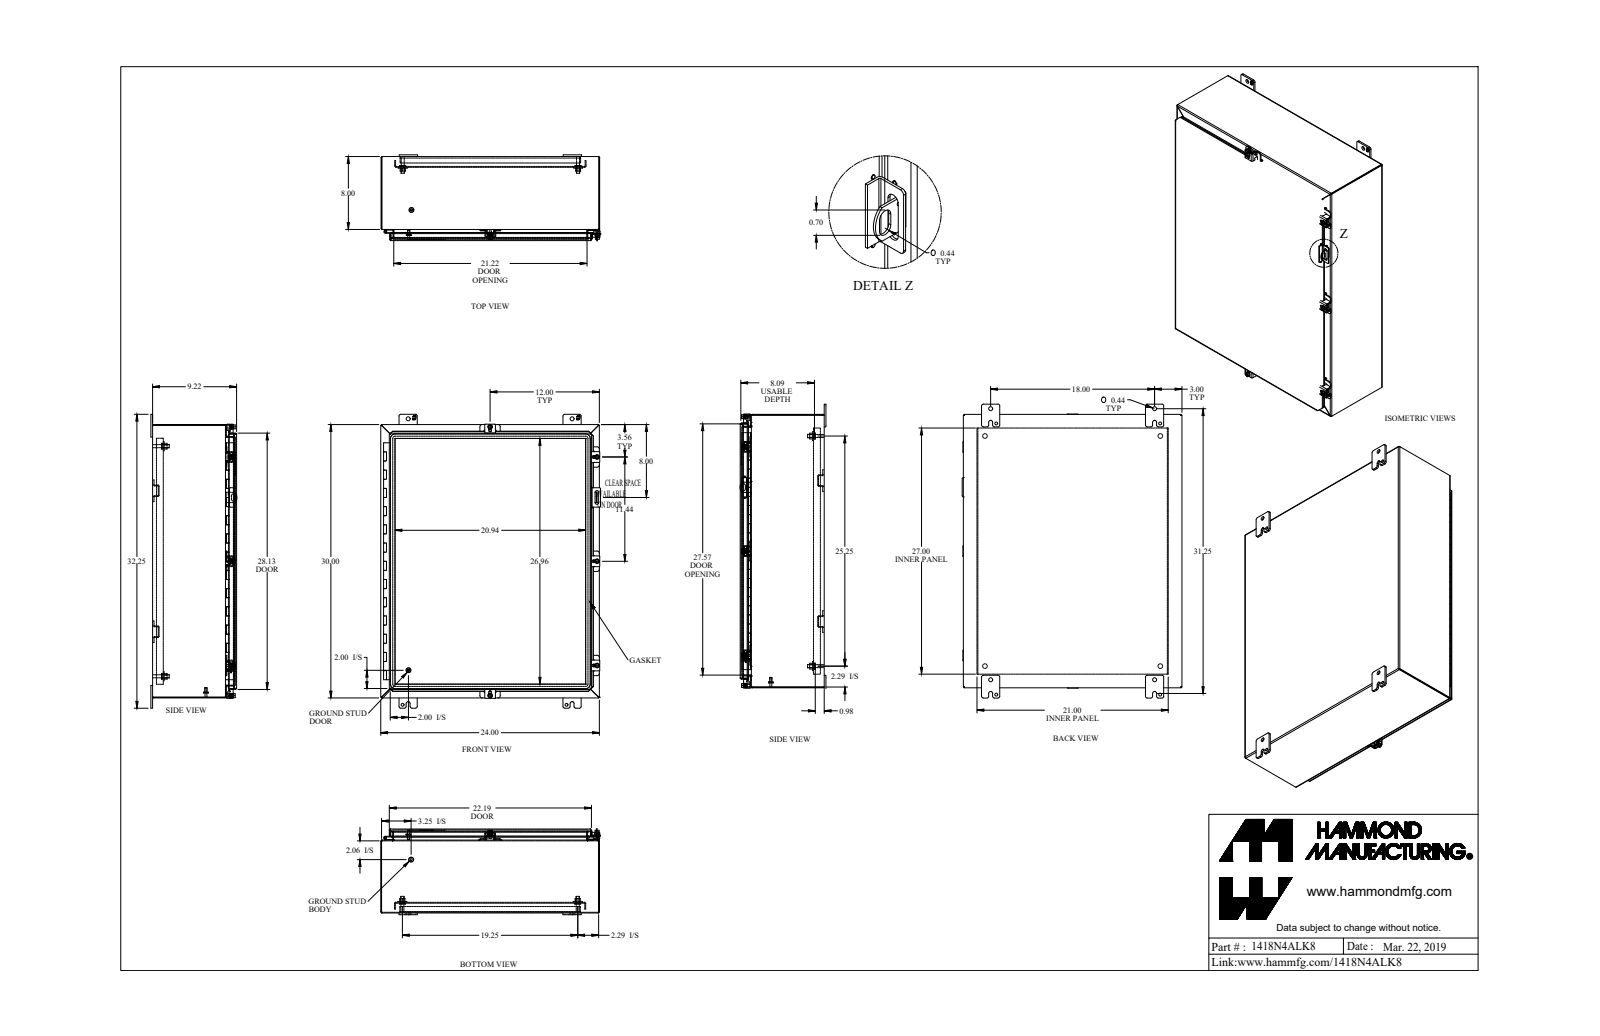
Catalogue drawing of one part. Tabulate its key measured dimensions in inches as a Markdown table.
| quantity | value |
| --- | --- |
| part name | 1418N4ALK8_Default |
| STEP written by | SolidWorks 2019 (CONFIG_CONTROL_DESIGN) |
| units | inches |
| bodies | 49 solids, 1795 faces (1059 planar, 612 cylindrical, 124 other) |
| overall size | 32.25 × 24.126 × 9.437 |
| volume | 305.3 in³ |
| surface area | 7 030 in² |
| round holes (diameter × count) | 0.232 × 5, 0.265 × 5, 0.375 × 5, 0.313 × 4, 0.437 × 4, 0.5 × 4, 0.307 × 2, 0.445 × 2, 0.125 × 1, 0.187 × 1 |
| round bosses / shafts (diameter × count) | 0.131 × 14, 0.5 × 5, 0.4 × 5, 0.244 × 5, 0.65 × 4, 0.375 × 4, 0.33 × 4, 1 × 2 |
| partial cylindrical surfaces (radius × count) | 0.05 × 26, 0.15 × 26, 0.188 × 24, 0.25 × 24, 0.041 × 16, 0.122 × 16, 0.125 × 11, 0.04 × 10 |
| main face-to-face distances | 0.081, 0.1, 9.041, 9.122, 9.141, 9.222, 0.095, 8.046, 7.946, 1.095 |
| hole center spacings | 29.018, 31.751, 1.736, 9.857, 18, 19.25, 29.75, 32.595 |
